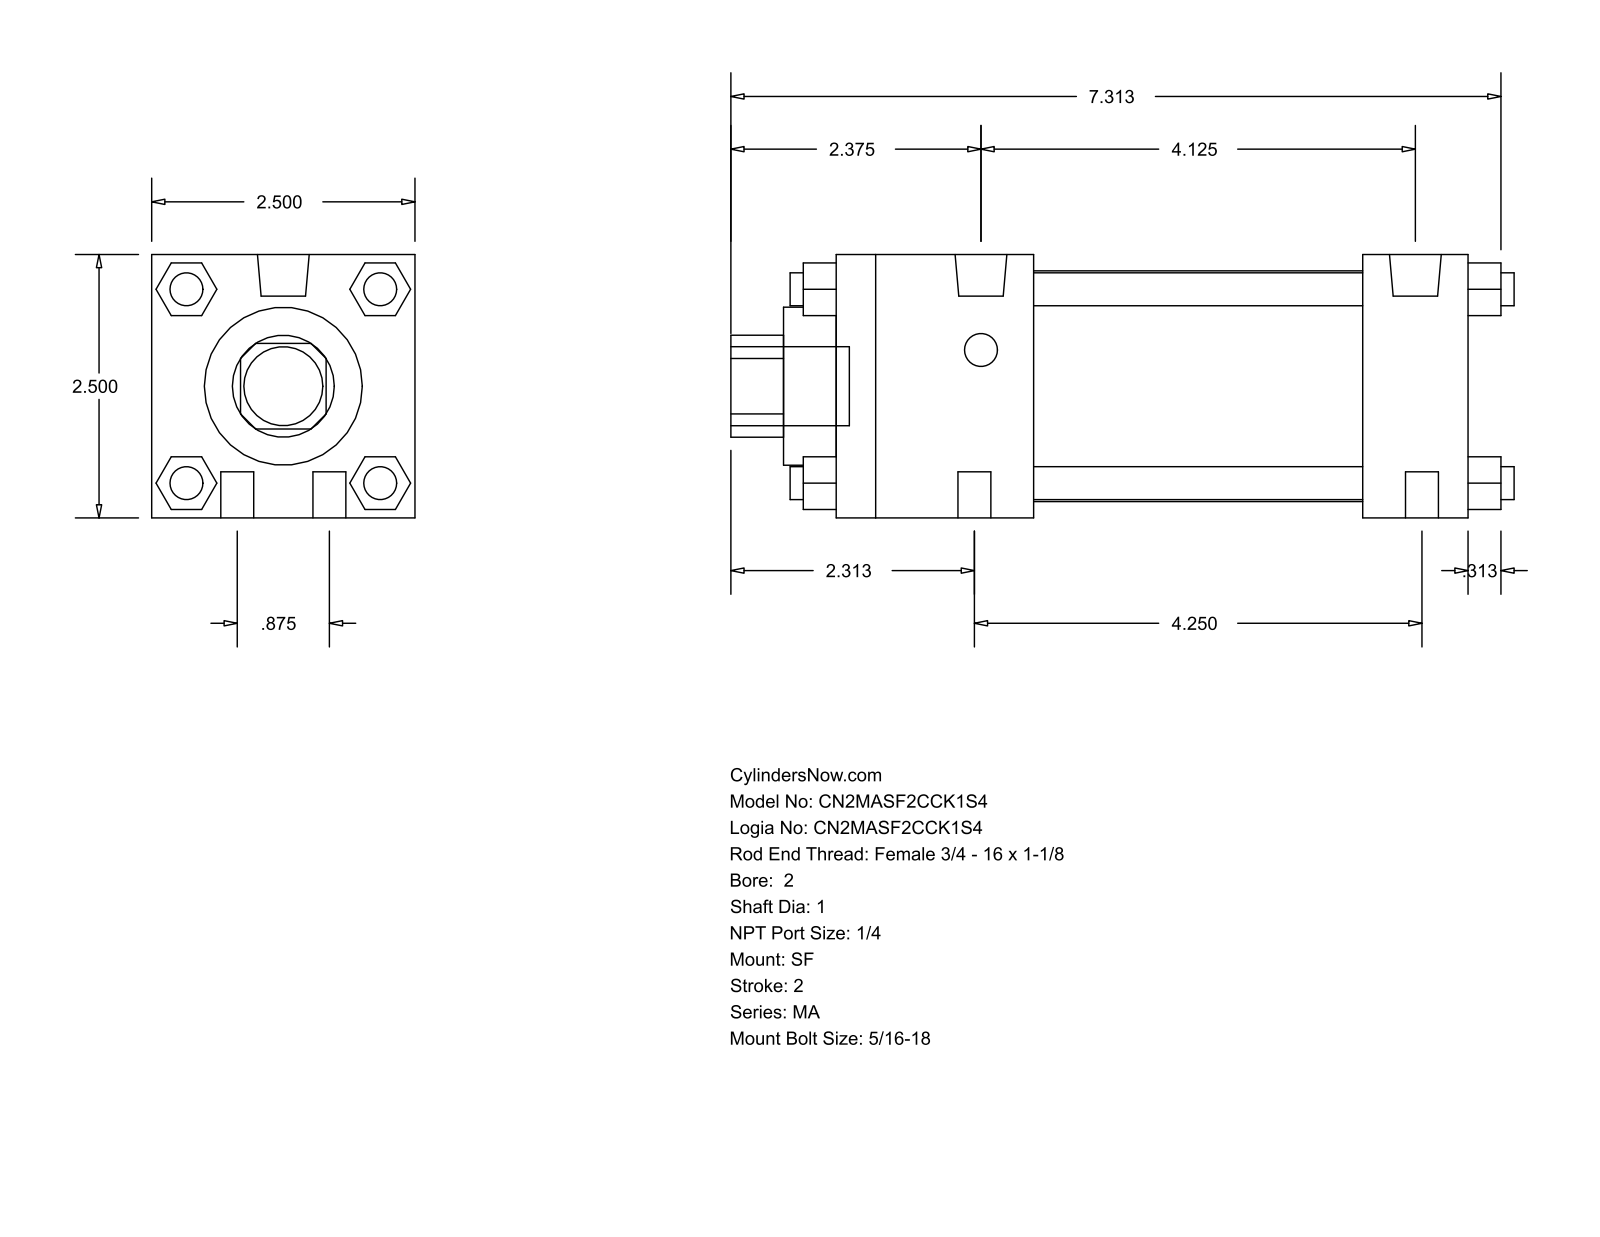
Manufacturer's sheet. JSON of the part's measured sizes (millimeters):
{"part_name": "MA_SF__0200_1", "step_written_by": "GSSL Pune (CONFIG_CONTROL_DESIGN)", "units": "millimeters", "bodies": {"solids": 0, "faces": 124, "planar": 94, "cylindrical": 30, "other": 0}, "overall_size": [188.91, 63.5, 63.5], "round_holes": [[25.4, 1], [38.1, 1], [55.63, 1]], "round_bosses_or_shafts": [[7.94, 10], [12.49, 2], [19.05, 1]], "partial_cylinders_radius": [[12.29, 1]], "face_to_face_distances": [63.5, 152.4, 12.7, 25.4, 127, 47.63, 79.37, 104.77, 40.47, 23.37]}
